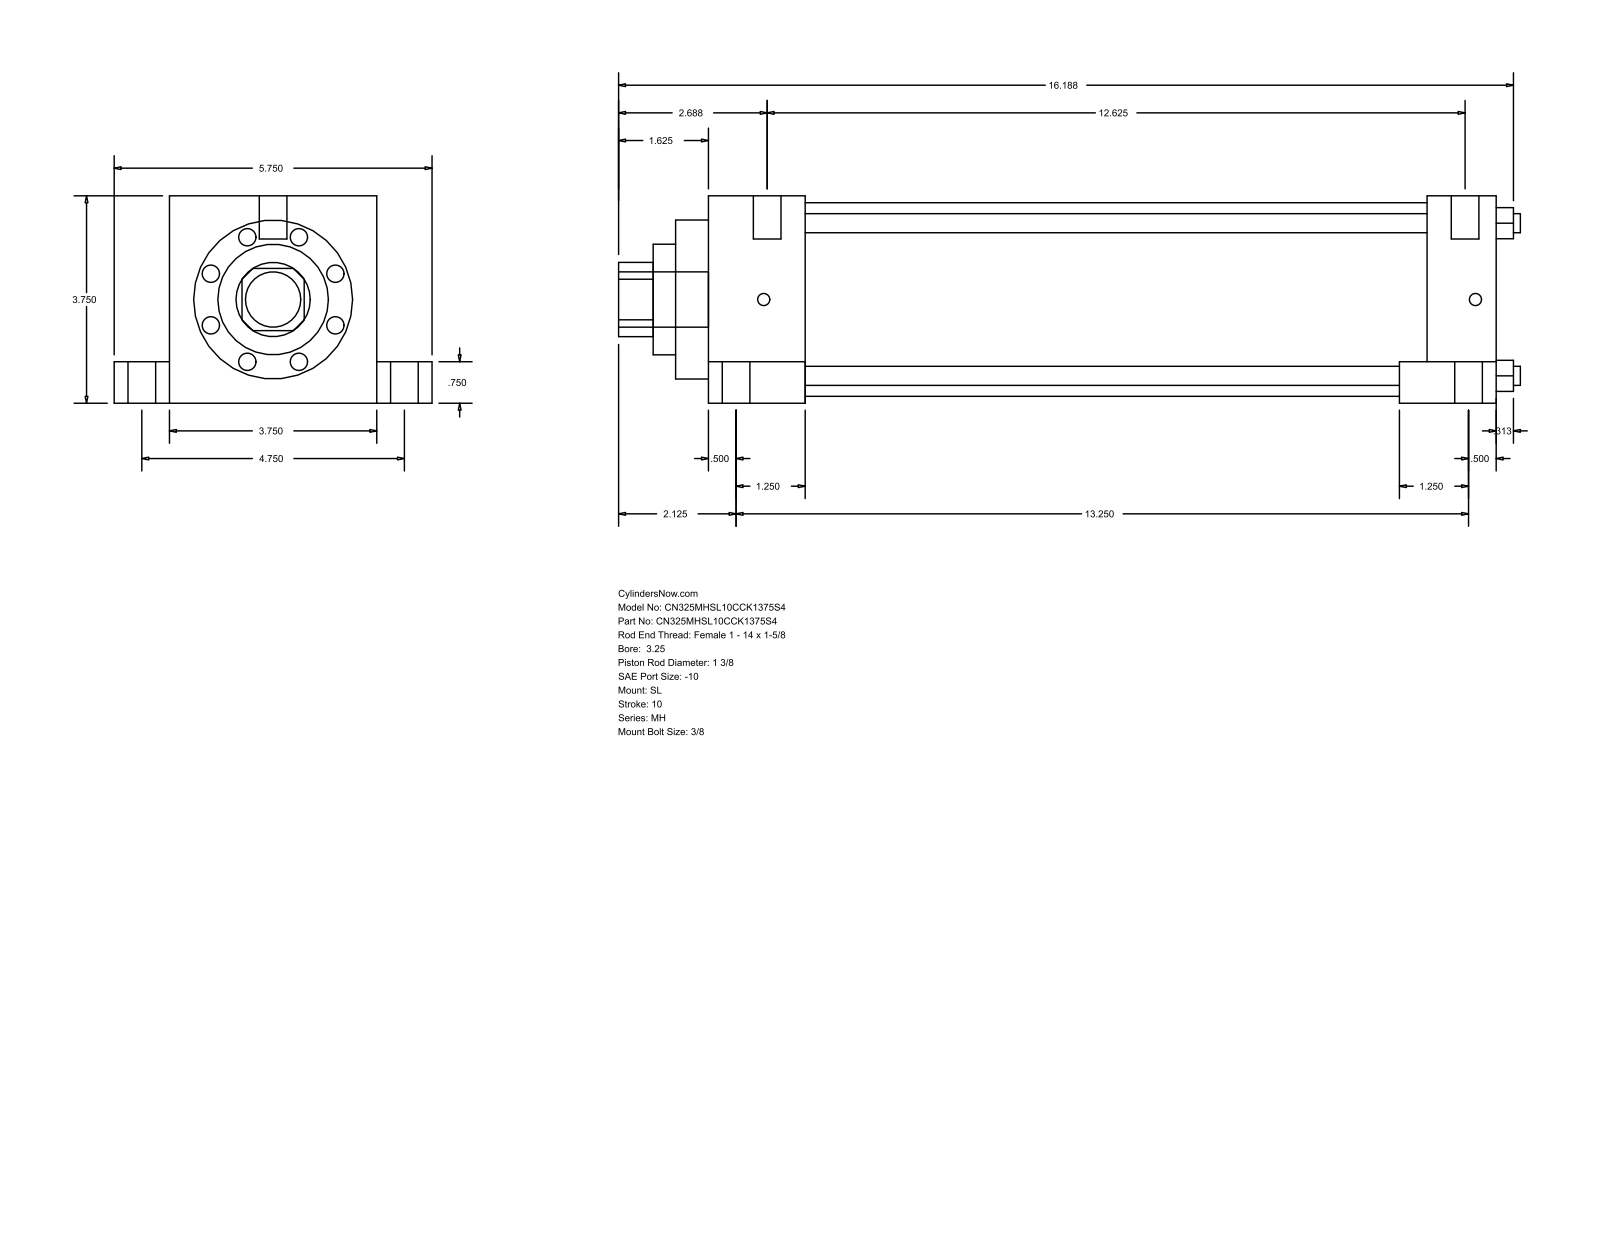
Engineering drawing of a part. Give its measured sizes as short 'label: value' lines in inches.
name: MH_SL__0325_1.375
written by: GSSL Pune (CONFIG_CONTROL_DESIGN)
unit: in
bodies: 0 solids, 110 faces (77 planar, 33 cylindrical, 0 other)
size: 16.313 × 5.75 × 3.75
holes: 4× ⌀0.345, 1× ⌀1.375, 1× ⌀2, 1× ⌀2.875, 1× ⌀3.5
bosses: 6× ⌀0.5, 4× ⌀0.75, 4× ⌀0.219, 1× ⌀1
rounds: 1× R0.672
face distances: 3.75, 14.25, 1.75, 12.5, 1, 4.75, 0.75, 3, 13, 11.25
hole spacings: 1.952, 2.76, 3.903
